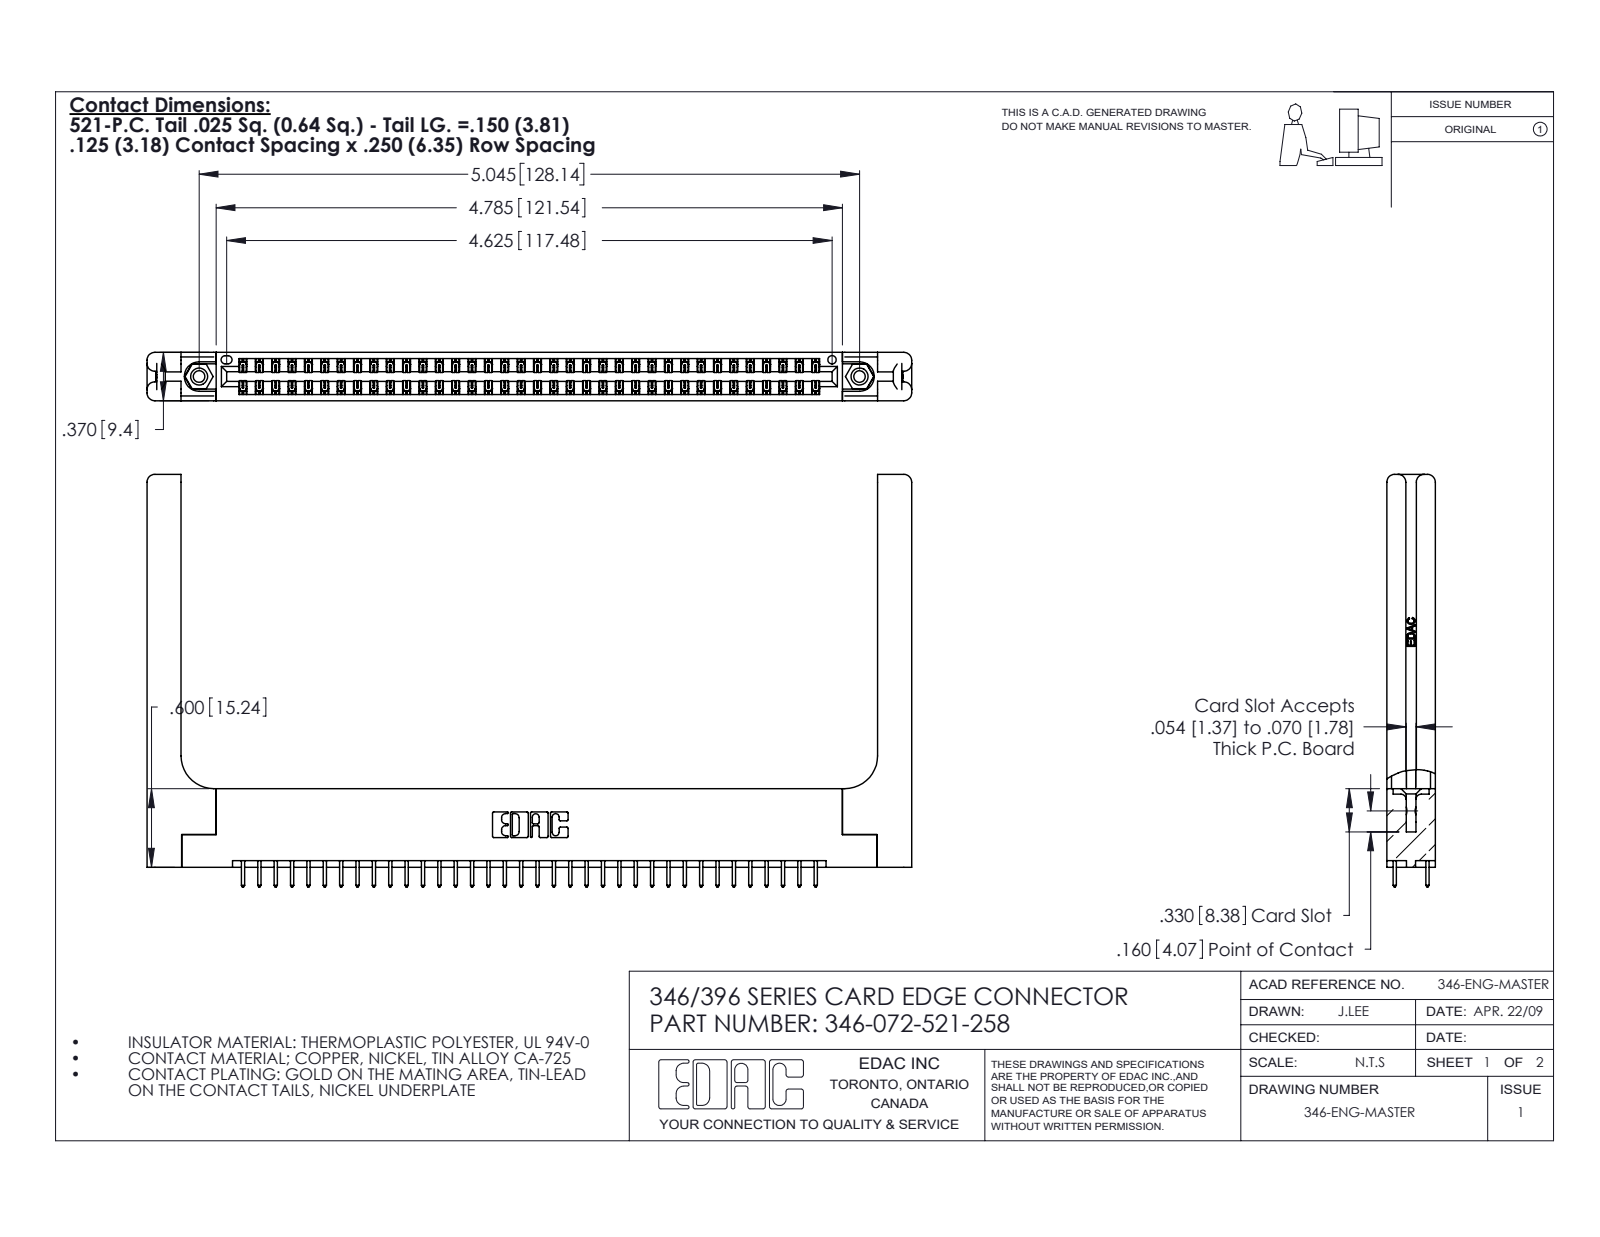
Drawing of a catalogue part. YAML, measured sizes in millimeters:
part_name: "346-072-521-258; 346 Part_Flush Mounting Lugs - 0.156 Dia-TH; 345-292-001_345-293-121; 346-220-058_345-220-058 (+1 more)"
step_written_by: "SolidWorks 2020 (CONFIG_CONTROL_DESIGN)"
units: millimeters
bodies: {solids: 77, faces: 4136, planar: 2758, cylindrical: 1318, other: 60}
overall_size: [148.4, 80, 9.4]
volume: 21860
surface_area: 24470
round_holes:
  - {diameter: 2.3, count: 2}
  - {diameter: 3.2, count: 2}
  - {diameter: 4, count: 2}
  - {diameter: 1.6, count: 1}
round_bosses_or_shafts:
  - {diameter: 3.9, count: 2}
partial_cylinders:
  - {radius: 0.2, count: 108}
  - {radius: 0.3, count: 72}
  - {radius: 0.3, count: 22}
  - {radius: 1.5, count: 16}
  - {radius: 0.2, count: 6}
  - {radius: 0.8, count: 6}
  - {radius: 0.7, count: 3}
  - {radius: 0.4, count: 2}
face_to_face_distances: [9.4, 1.2, 8.2, 1.8, 3.8, 3.8, 6.4, 0.6, 7.6, 7]
hole_center_spacings: [6.2, 122.8, 128.1]
